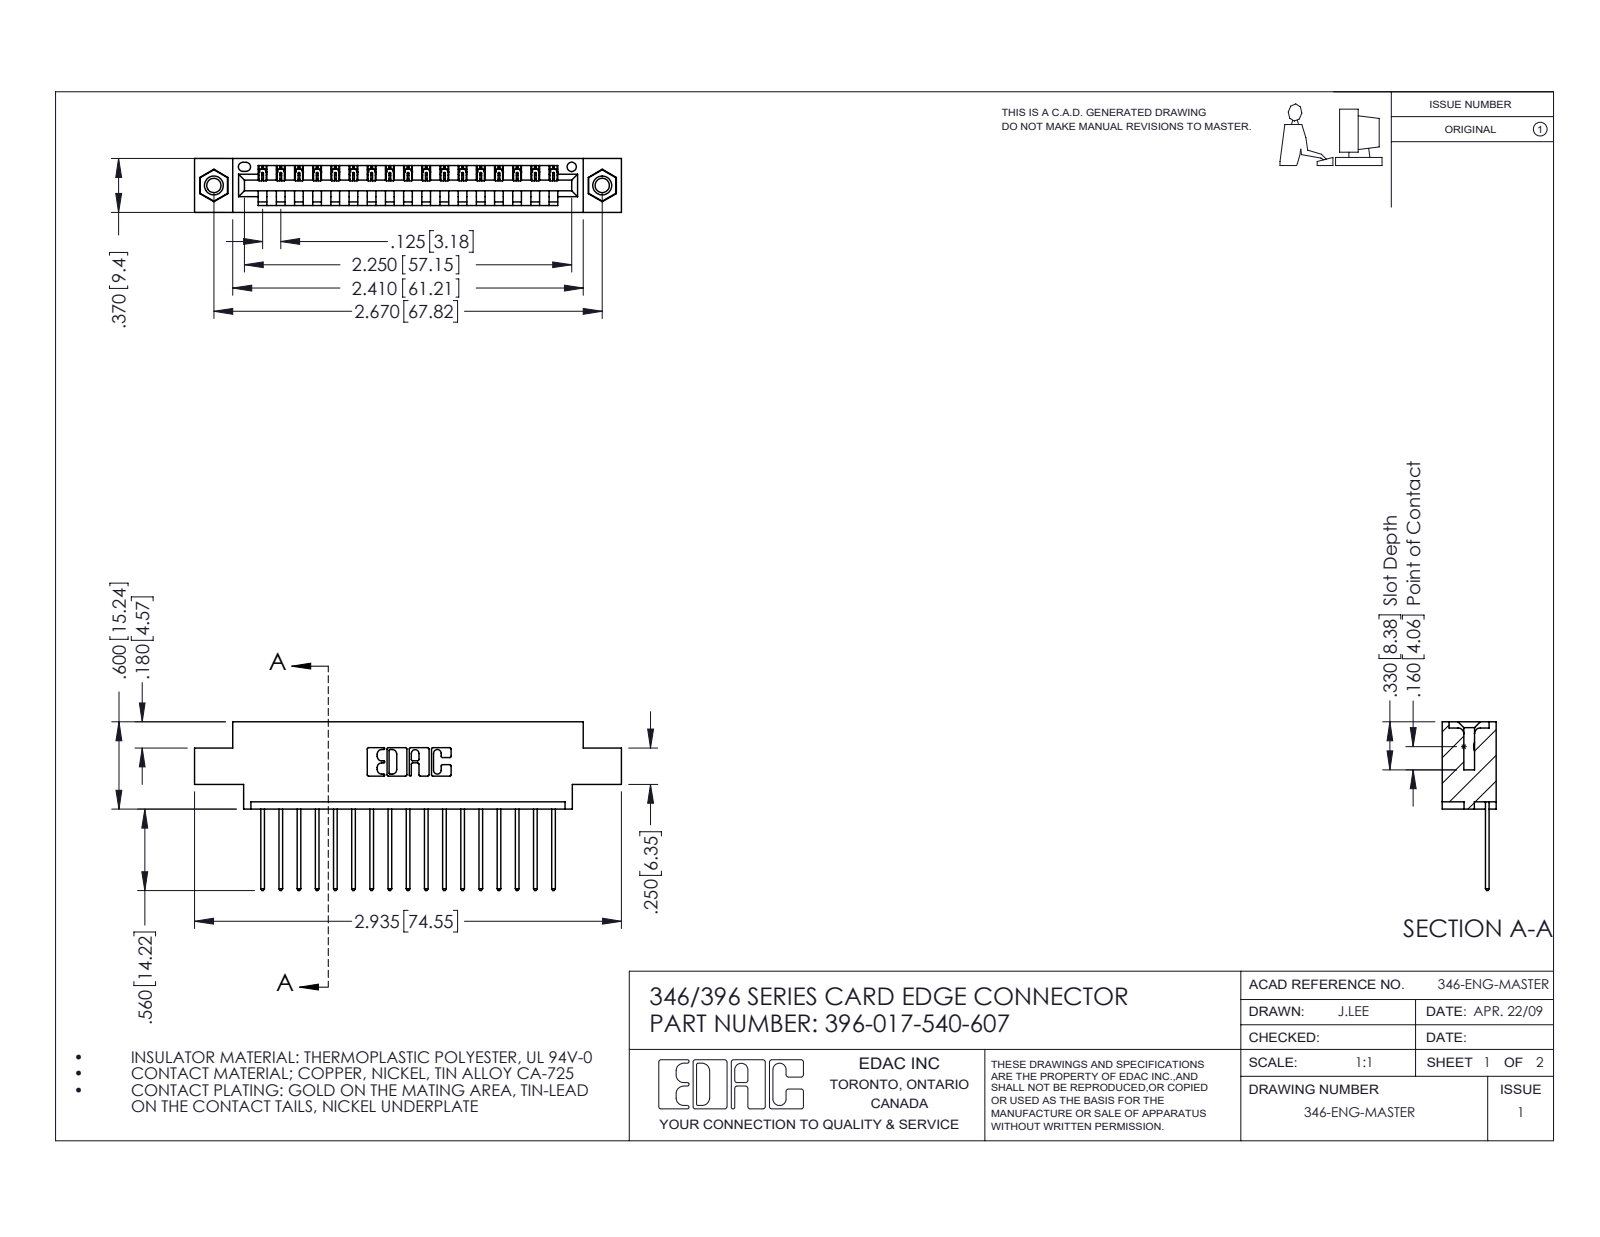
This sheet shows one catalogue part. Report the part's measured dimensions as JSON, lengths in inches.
{"part_name": "345-250-001_345-250-005-103; 396-017-540-607; 346 Part_0.170 Offset - 0.156 Dia-TI; 345-292-001_345-293-140", "step_written_by": "SolidWorks 2016 (CONFIG_CONTROL_DESIGN)", "units": "inches", "bodies": {"solids": 20, "faces": 1172, "planar": 792, "cylindrical": 364, "other": 16}, "overall_size": [2.935, 1.16, 0.37], "volume_in3": 0.416, "surface_area_in2": 13.35, "round_holes": [[0.098, 2], [0.125, 2], [0.156, 2], [0.064, 1]], "round_bosses_or_shafts": [[0.155, 2]], "partial_cylinders_radius": [[0.006, 34], [0.01, 34], [0.01, 22], [0.007, 6], [0.031, 6], [0.026, 3], [0.031, 2], [0.04, 2]], "face_to_face_distances": [0.048, 0.322, 0.37, 0.25, 0.072, 0.298, 0.025, 0.222, 0.148, 0.1], "hole_center_spacings": [0.246, 2.463, 2.67]}
